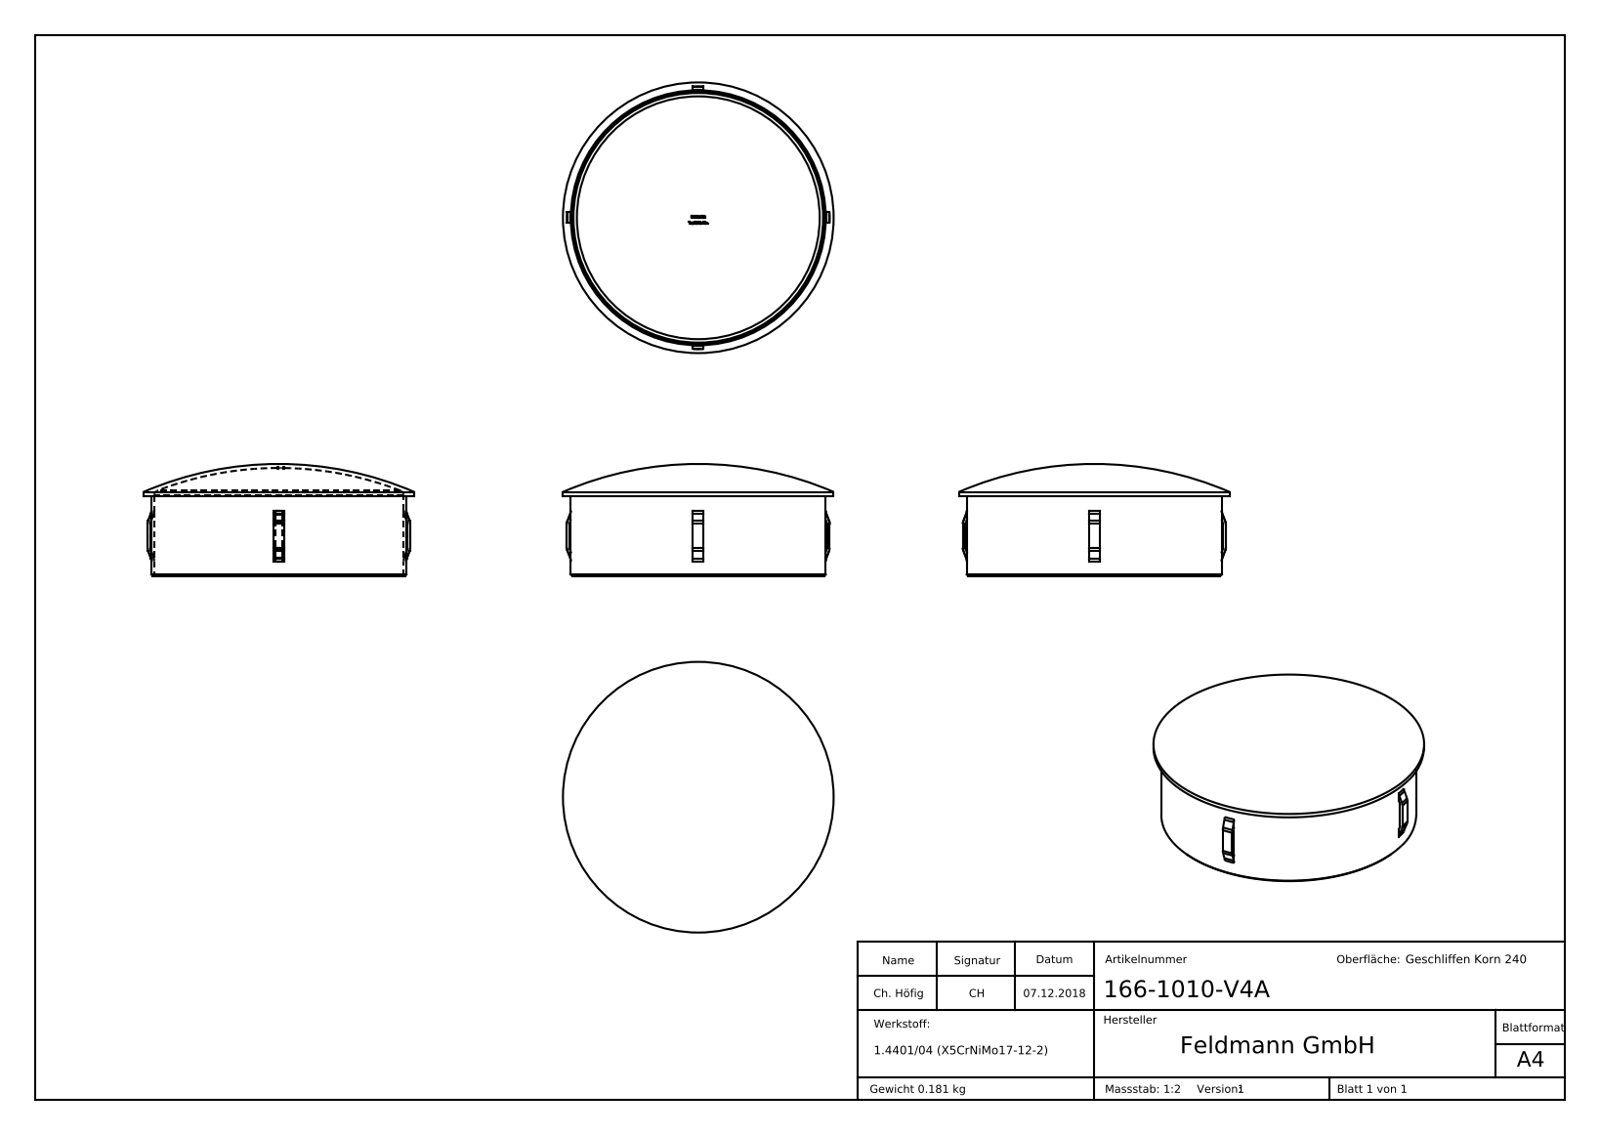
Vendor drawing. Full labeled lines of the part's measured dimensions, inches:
Part name (STEP PRODUCT): 166-1010-V4A
STEP written by: SolidWorks 2015 (CONFIG_CONTROL_DESIGN)
Units: inches
Bodies: 1 solid, 341 faces (135 planar, 16 cylindrical, 190 other)
Overall size (bounding box): 4 × 4 × 1.654
Volume: 1.38 in³ · Surface area: 55.51 in²
Round holes (diameter × count): ⌀3.689 ×1
Round bosses / shafts (diameter × count): ⌀4 ×1, ⌀3.768 ×1
Partial cylindrical surfaces — rounded edges, fillets, slot ends (radius × count): R1.904 ×1, R1.943 ×1
Main face-to-face distances: 1.181, 0.03, 0.128, 0.157, 0.098, 0.049, 0.078, 0.03, 0.105, 0.021
